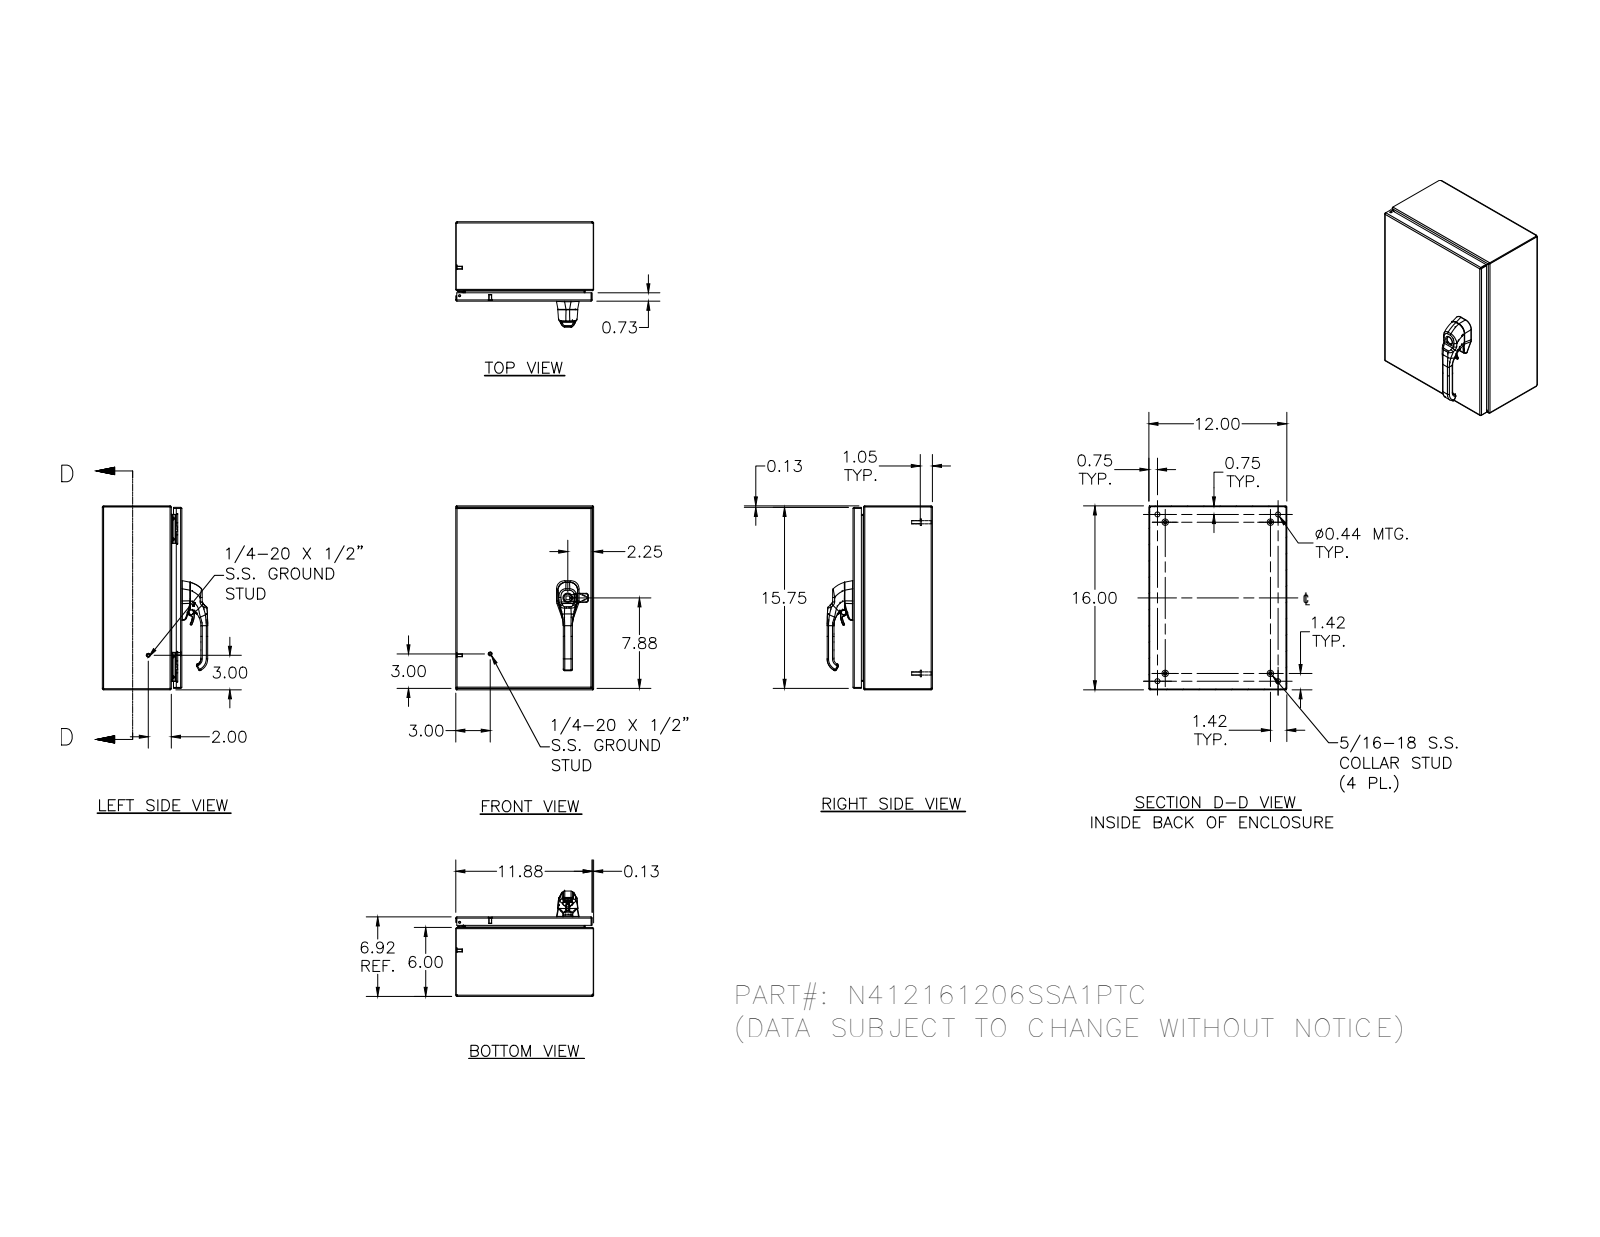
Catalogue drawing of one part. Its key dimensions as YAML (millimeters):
part_name: "N412161206SSA1PTC; N412161206SSA1PTCBKP; N4121612SSA1PTCLID; HFW328176 (+8 more)"
step_written_by: "Autodesk Inventor 2012 (AUTOMOTIVE_DESIGN)"
units: millimeters
bodies: {solids: 41, faces: 2784, planar: 882, cylindrical: 1037, other: 865}
overall_size: [406.4, 304.8, 232.8]
volume: 1134000
surface_area: 1152000
round_holes:
  - {diameter: 4.8, count: 5}
  - {diameter: 2.4, count: 4}
  - {diameter: 3.9, count: 4}
  - {diameter: 4.2, count: 4}
  - {diameter: 4.4, count: 4}
  - {diameter: 11.1, count: 4}
  - {diameter: 5.4, count: 3}
  - {diameter: 7.1, count: 3}
  - {diameter: 4, count: 2}
  - {diameter: 8, count: 2}
  - {diameter: 10.2, count: 2}
  - {diameter: 10.5, count: 2}
round_bosses_or_shafts:
  - {diameter: 6.4, count: 10}
  - {diameter: 14.3, count: 4}
  - {diameter: 9.1, count: 4}
  - {diameter: 8.1, count: 4}
  - {diameter: 7.6, count: 4}
  - {diameter: 7, count: 4}
  - {diameter: 6.5, count: 4}
  - {diameter: 4.2, count: 4}
partial_cylinders:
  - {radius: 0.5, count: 173}
  - {radius: 0.3, count: 101}
  - {radius: 0.8, count: 30}
  - {radius: 1.3, count: 26}
  - {radius: 0.5, count: 21}
  - {radius: 2.7, count: 20}
  - {radius: 0.4, count: 18}
  - {radius: 2, count: 14}
face_to_face_distances: [1.9, 173.8, 302.9, 175.7, 171.9, 404.5, 301, 304.8, 406.4, 402.6]
hole_center_spacings: [304.7, 0.4, 16.8, 321.5, 0.5, 12.7, 16.5, 16.7]
